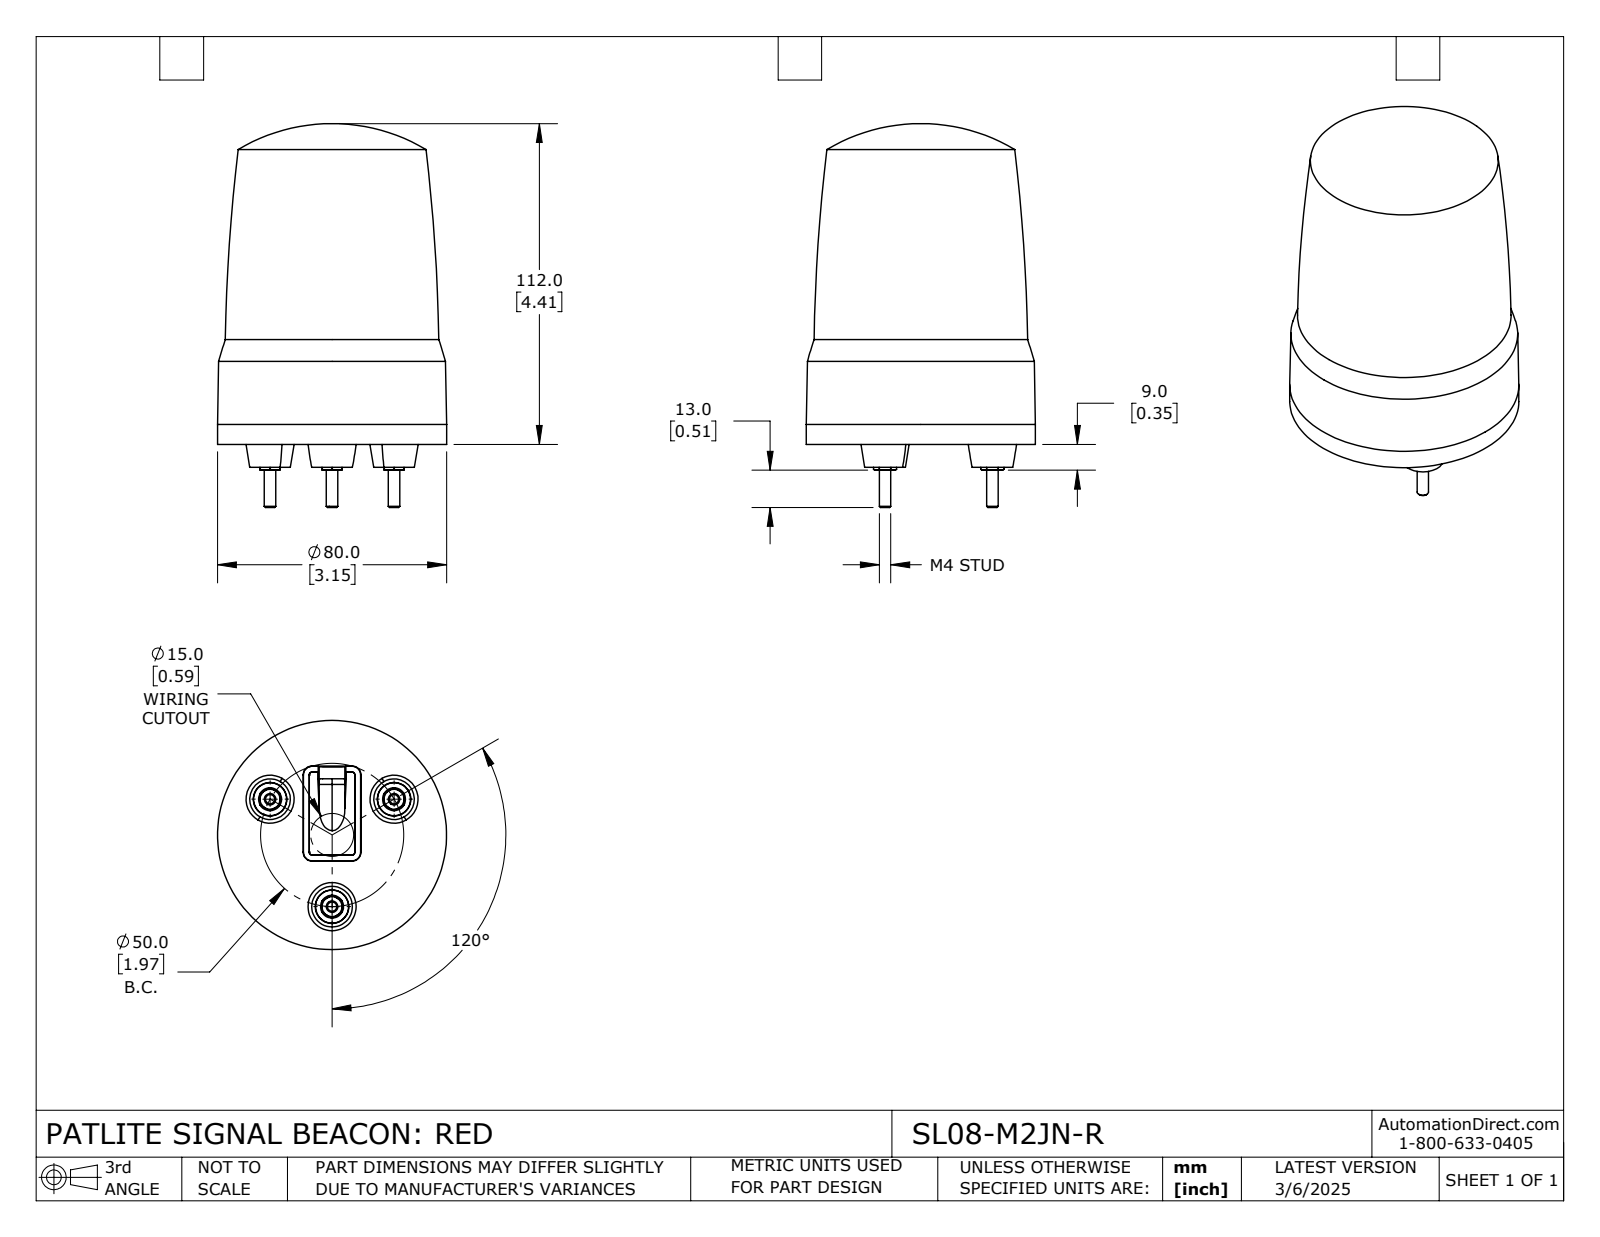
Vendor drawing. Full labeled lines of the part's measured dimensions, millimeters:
Part name (STEP PRODUCT): SL08-M2JN-R
STEP written by: SolidWorks 2024 (CONFIG_CONTROL_DESIGN)
Units: millimetres
Bodies: 1 solid, 138 faces (47 planar, 14 cylindrical, 77 other)
Overall size (bounding box): 134 × 80 × 80
Volume: 463 225 mm³ · Surface area: 35 408 mm²
Round bosses / shafts (diameter × count): ⌀8 ×3, ⌀4 ×3, ⌀80 ×1
Main face-to-face distances: 0.85, 2.45, 1.6, 5.3, 6.15, 7.75, 2.7, 8, 8.85, 10.45
